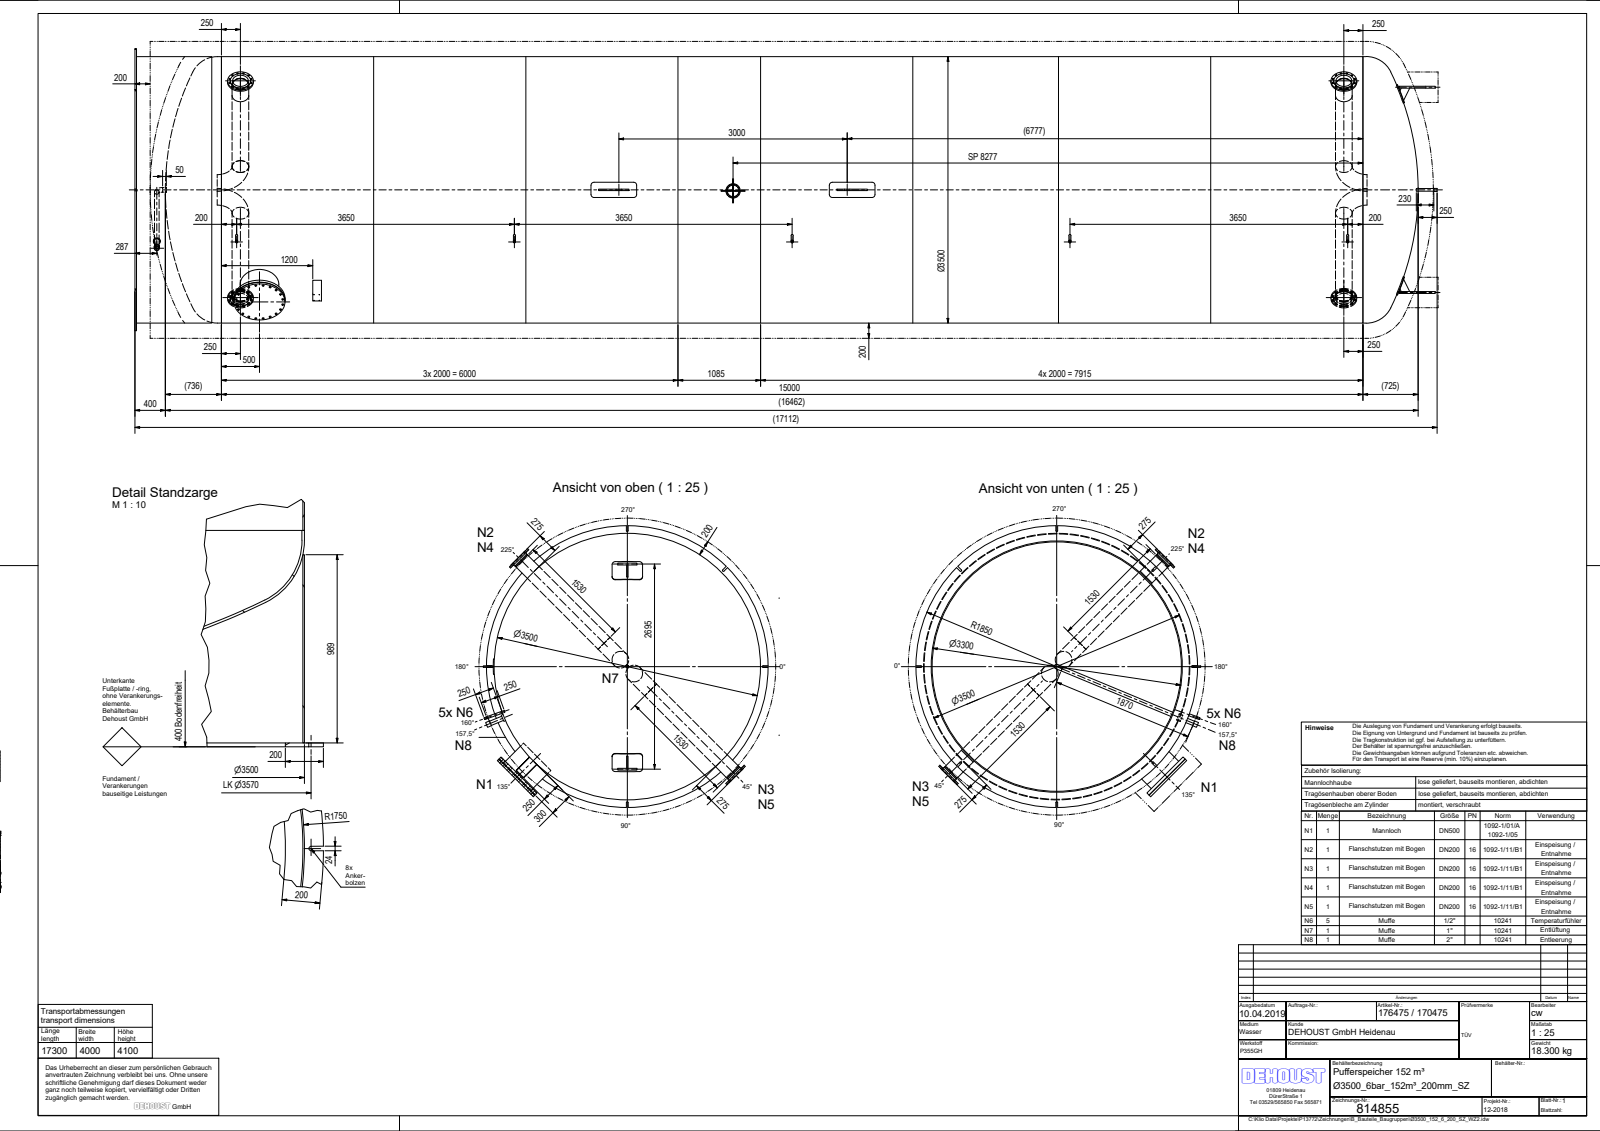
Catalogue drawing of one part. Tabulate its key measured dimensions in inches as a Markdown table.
| quantity | value |
| --- | --- |
| part name | Ø3500_152_6_200_SZ_WZ2; Klöpper_Gew_Ø3500_10,6; Klöpper_Gew_Ø3500_13,0; Zyl_Ø3500_8x15000_2019 (+8 more) |
| STEP written by | Autodesk Inventor 2019 (AUTOMOTIVE_DESIGN) |
| units | inches |
| bodies | 50 solids, 426 faces (172 planar, 226 cylindrical, 28 other) |
| overall size | 673.691 × 147.321 × 145.666 |
| volume | 135 700 in³ |
| surface area | 664 300 in² |
| round holes (diameter × count) | 0.866 × 48, 1.024 × 40, 0.733 × 5, 0.854 × 5, 1.059 × 5, 0.228 × 4, 8.13 × 4, 8.161 × 4, 8.626 × 4, 2.059 × 2, 2.835 × 2, 1.075 × 1 |
| round bosses / shafts (diameter × count) | 8.626 × 8, 1.059 × 5, 1.039 × 5, 13.386 × 4, 10.551 × 4, 26.378 × 2, 145.669 × 1, 137.795 × 1 |
| partial cylindrical surfaces (radius × count) | 0.472 × 8, 1.575 × 8, 1.654 × 8, 0.197 × 2, 0.394 × 2, 2.835 × 2, 4.921 × 1, 69.37 × 1 |
| main face-to-face distances | 0.787, 23.622, 7.52, 6.733, 7.874, 7.087, 0.354, 273.622, 316.929, 318.36 |
| hole center spacings | 12.205, 5.807, 143.701, 7.543, 21.749, 287.402, 23.215, 5.807 |
